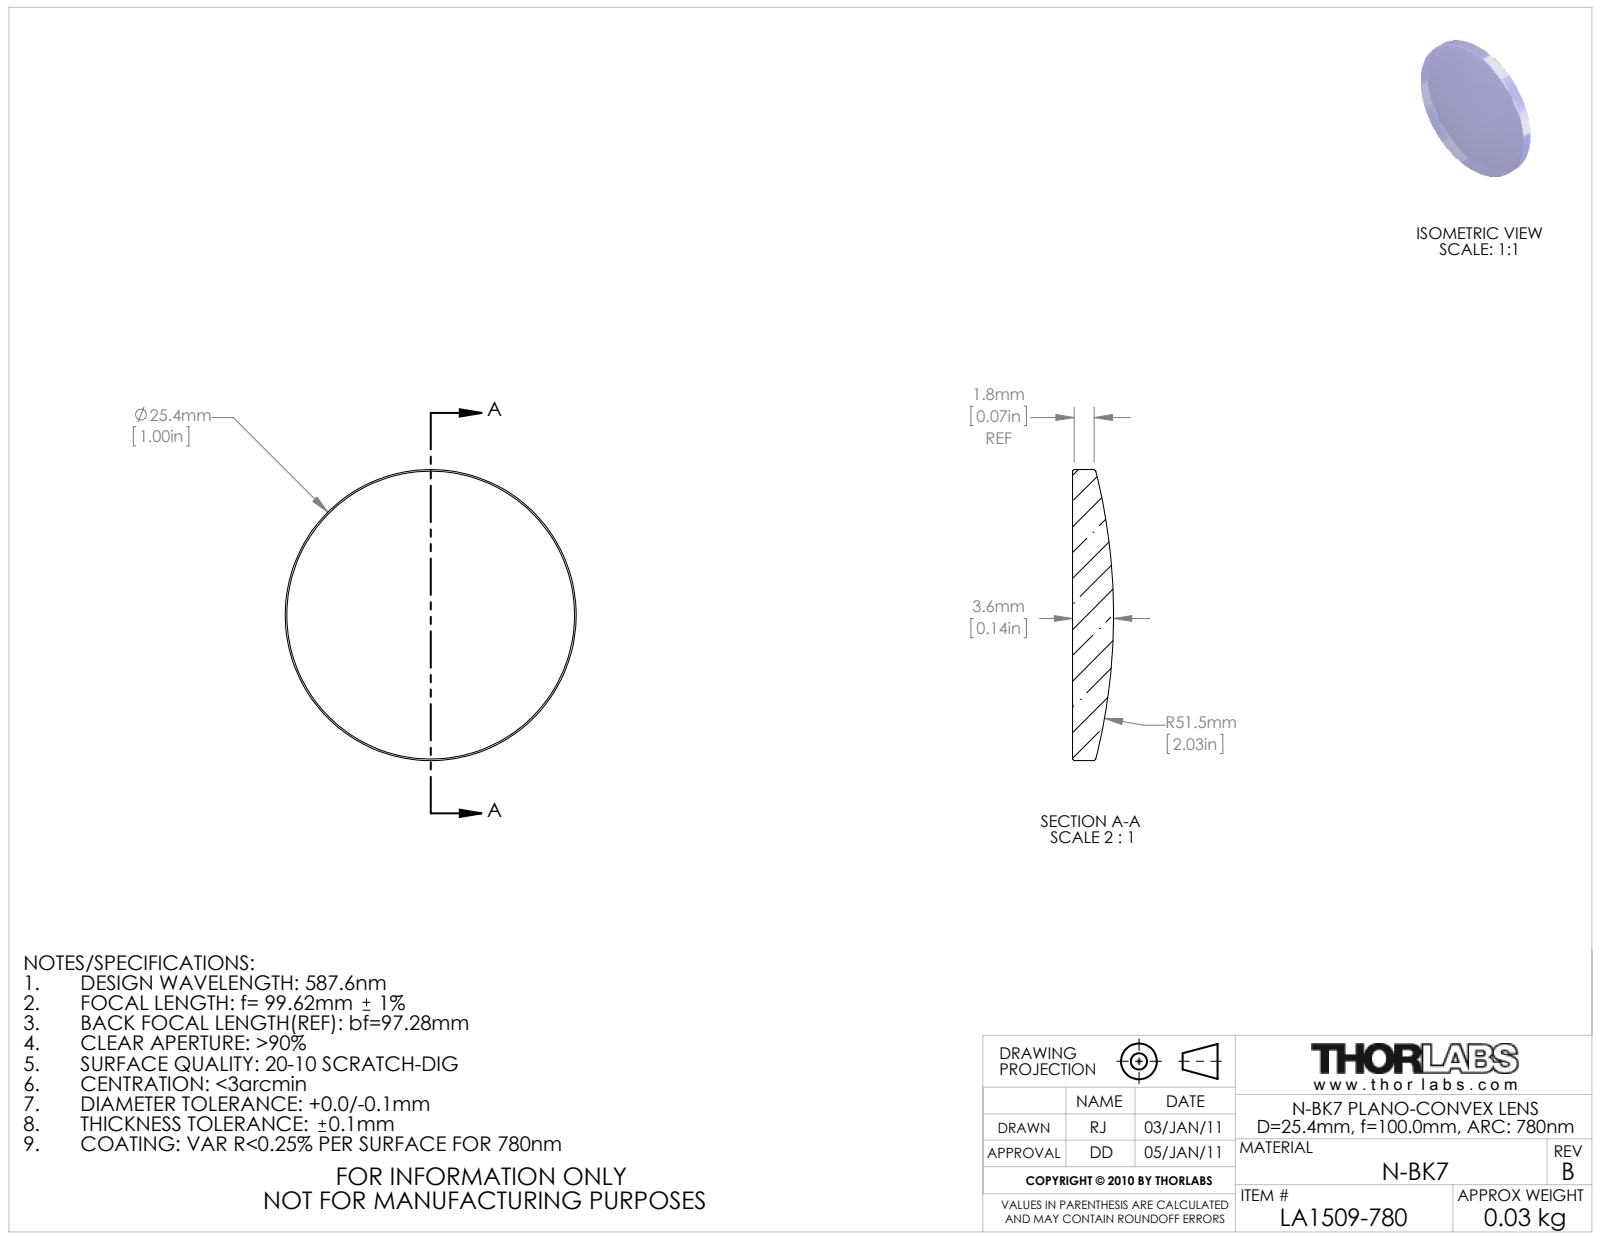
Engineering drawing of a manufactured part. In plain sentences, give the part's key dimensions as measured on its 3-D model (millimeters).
The part is named "21793-E0W". Its 3-D file was written by "SolidWorks 2011 (AUTOMOTIVE_DESIGN)". It is 0 solids with 9 faces: 1 planar, 2 cylindrical and 6 other. Overall it measures 25.4 by 25.4 by 3.59 millimeters. Round bosses or shafts: 1 of diameter 25.4.
